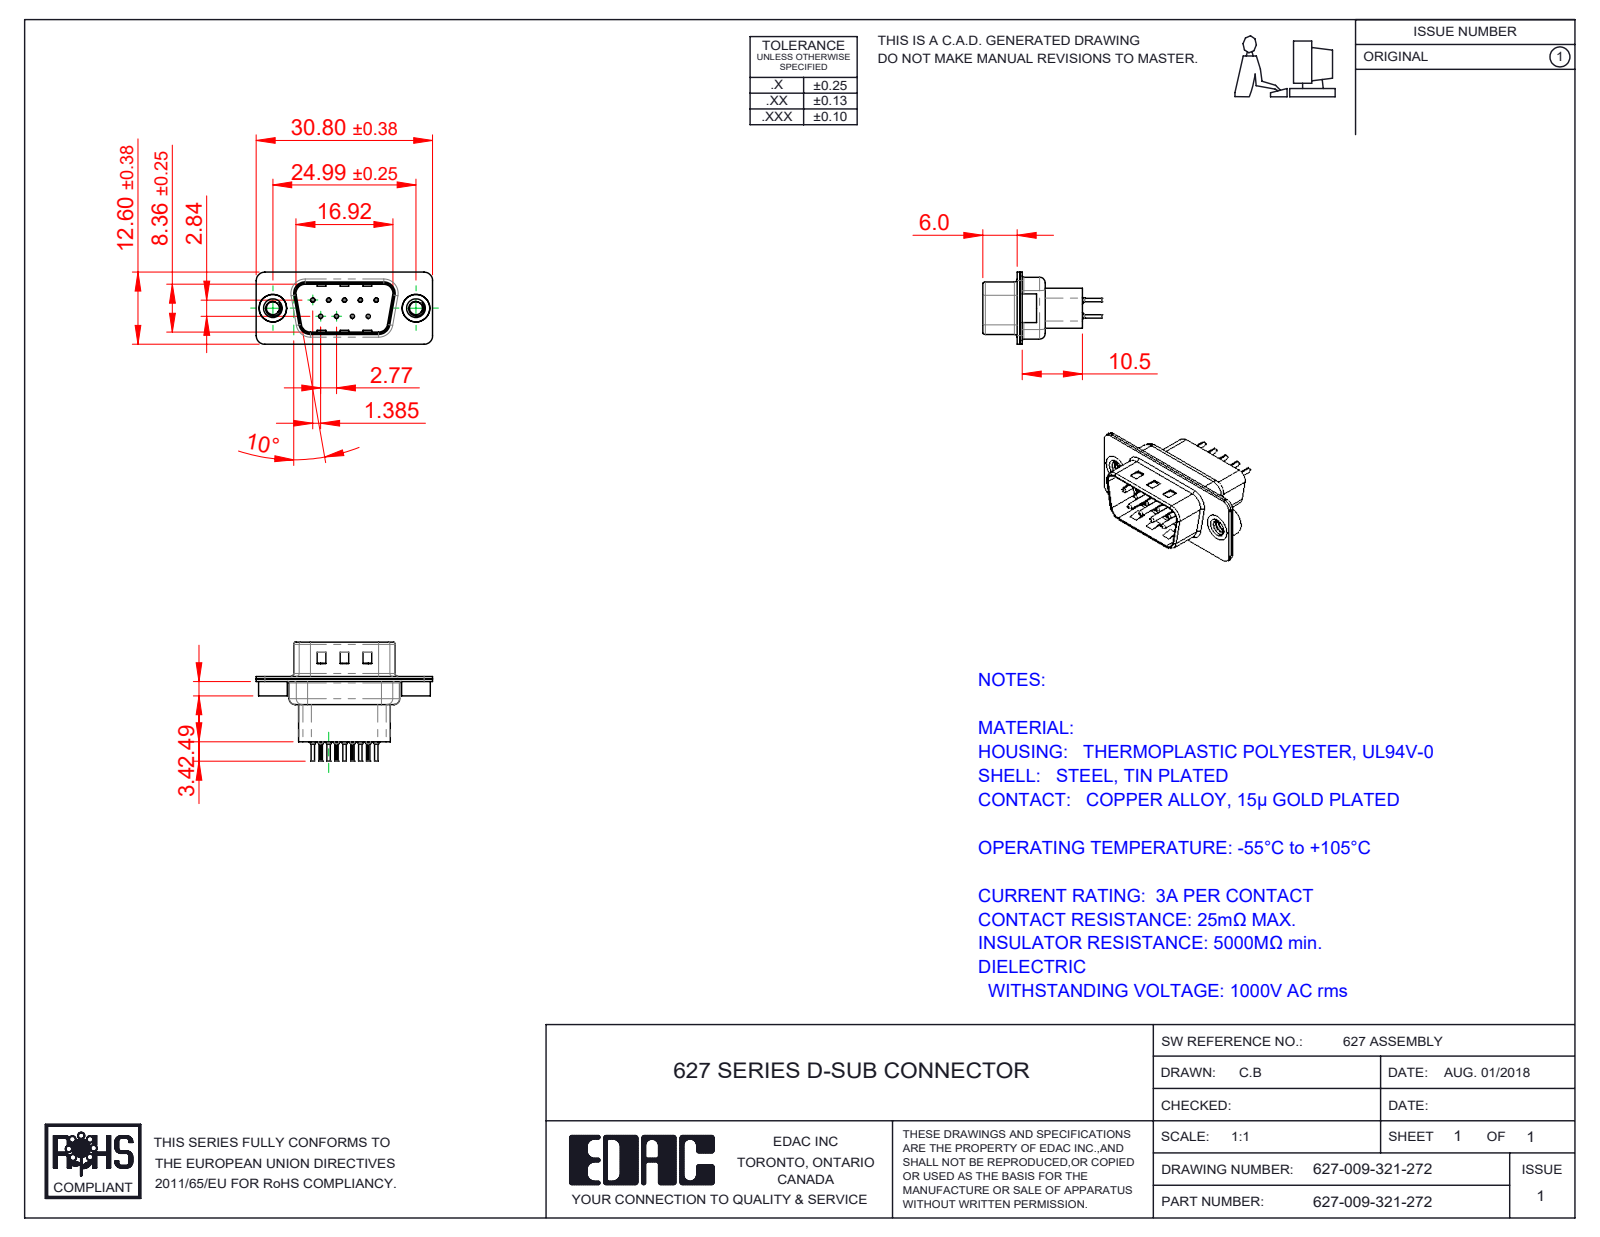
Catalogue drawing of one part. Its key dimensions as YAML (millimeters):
part_name: "627 Contact Row 2_21H; 627-009-321-072; 627 Housing_09 HP; 627 Shell Front_09 Contacts (+3 more)"
step_written_by: "SolidWorks 2020 (CONFIG_CONTROL_DESIGN)"
units: millimeters
bodies: {solids: 14, faces: 1182, planar: 323, cylindrical: 460, other: 399}
overall_size: [30.8, 20.8, 12.6]
volume: 1767
surface_area: 4688
round_holes:
  - {diameter: 0.2, count: 9}
  - {diameter: 0.35, count: 9}
  - {diameter: 1.1, count: 9}
  - {diameter: 1.6, count: 9}
  - {diameter: 2.26, count: 2}
  - {diameter: 4, count: 2}
  - {diameter: 4.8, count: 2}
round_bosses_or_shafts:
  - {diameter: 2, count: 9}
  - {diameter: 1.5, count: 9}
  - {diameter: 0.75, count: 9}
  - {diameter: 0.6, count: 9}
  - {diameter: 5, count: 2}
  - {diameter: 4.9, count: 2}
partial_cylinders:
  - {radius: 0.1, count: 18}
  - {radius: 1.5, count: 18}
  - {radius: 2, count: 12}
  - {radius: 0.5, count: 8}
  - {radius: 1.6, count: 8}
  - {radius: 0.25, count: 4}
  - {radius: 0.6, count: 4}
  - {radius: 0.65, count: 4}
face_to_face_distances: [0.45, 0.4, 0.9, 0.82, 9.58, 1.4, 1.5, 0.68, 7.68, 1.08]
hole_center_spacings: [3.16, 2.77, 5.54, 5.03, 5.04, 8.31, 7.48, 7.49]
